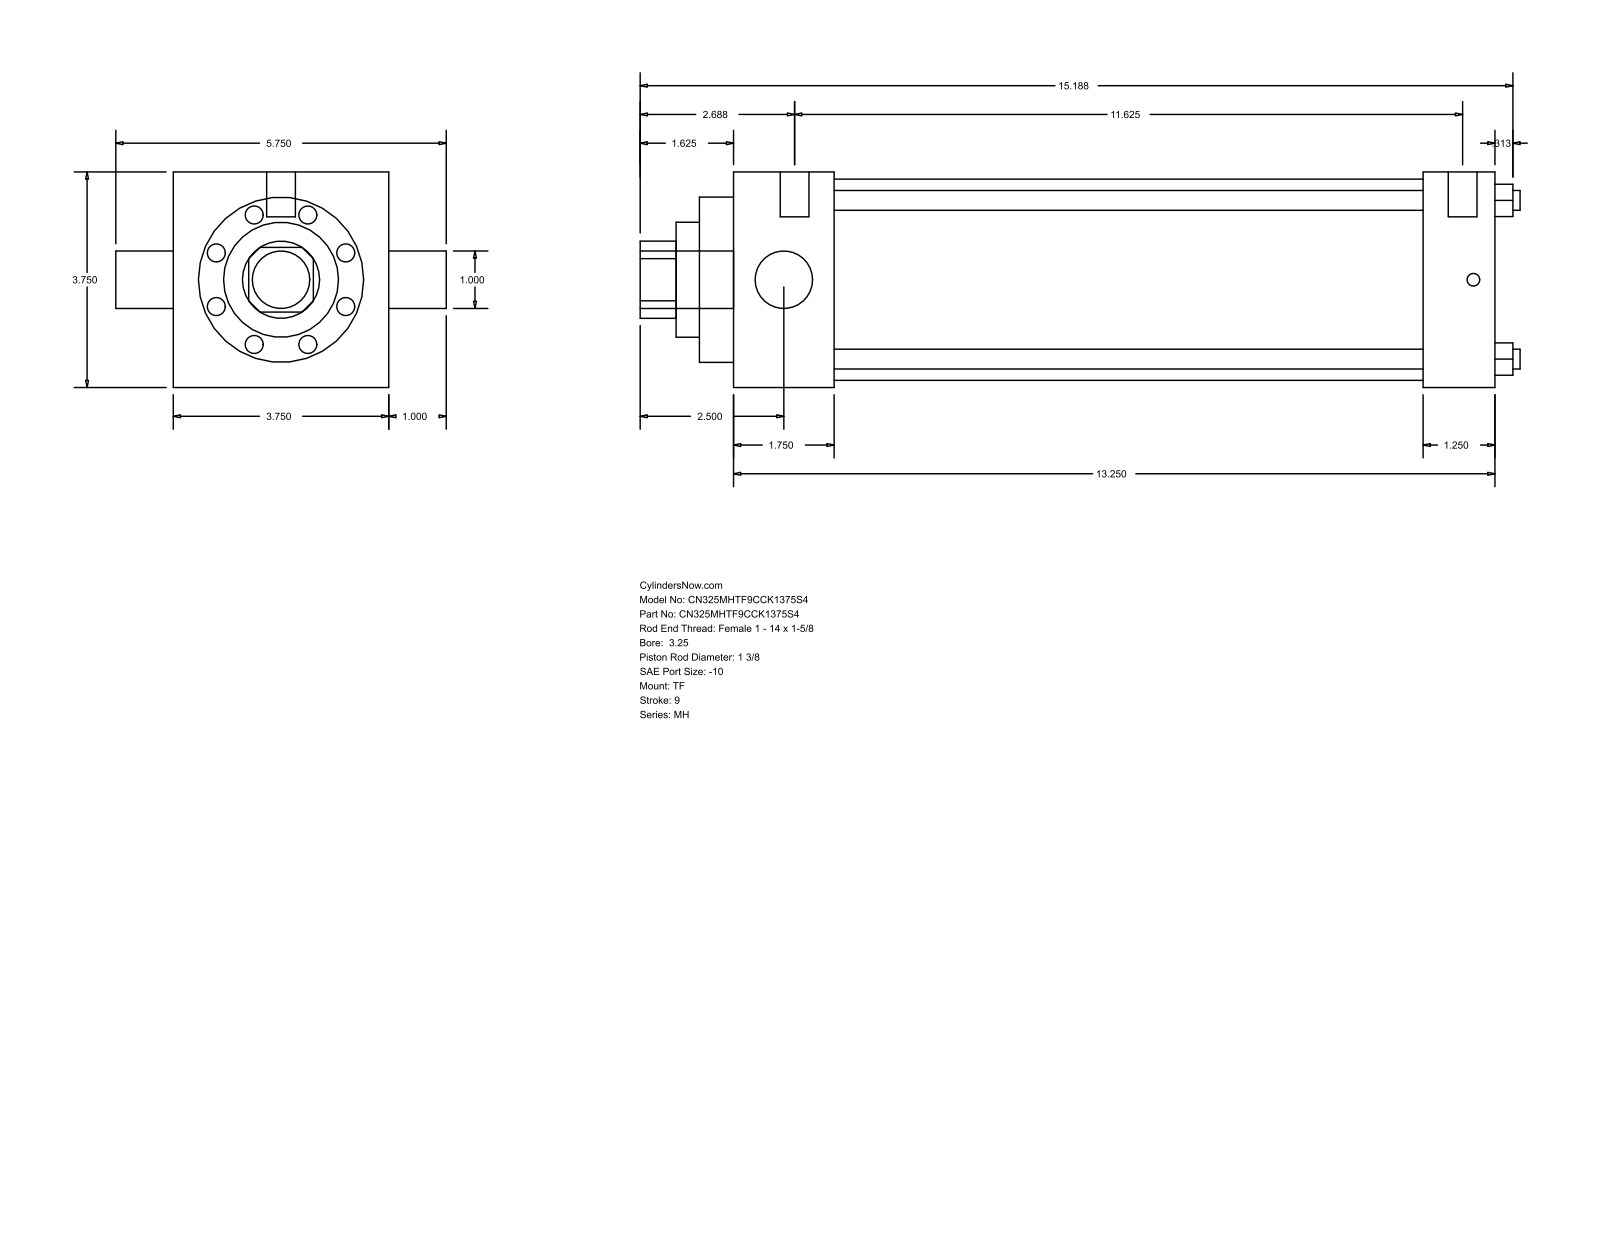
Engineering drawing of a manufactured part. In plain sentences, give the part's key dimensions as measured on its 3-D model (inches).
The part is named "MH_TF__0325_1.375". Its 3-D file was written by "GSSL Pune (CONFIG_CONTROL_DESIGN)". It is 0 solids with 86 faces: 61 planar, 25 cylindrical and 0 other. Overall it measures 15.313 by 5.75 by 3.75 inches. Round holes: 4 of diameter 0.345, 1 of diameter 1, 1 of diameter 1.375, 1 of diameter 2, 1 of diameter 2.875, 1 of diameter 3.5. Round bosses or shafts: 3 of diameter 0.219, 2 of diameter 0.5, 1 of diameter 1. Partial cylindrical surfaces (rounded edges, fillets, slot ends): 1 of radius 0.672. The main face-to-face distances are 3.75, 13.25, 1.75, 12, 10.25, 11.5, 1.25, 0.594, 2.344, 12.594. The hole center spacings are 1.952, 2.76, 3.903.
